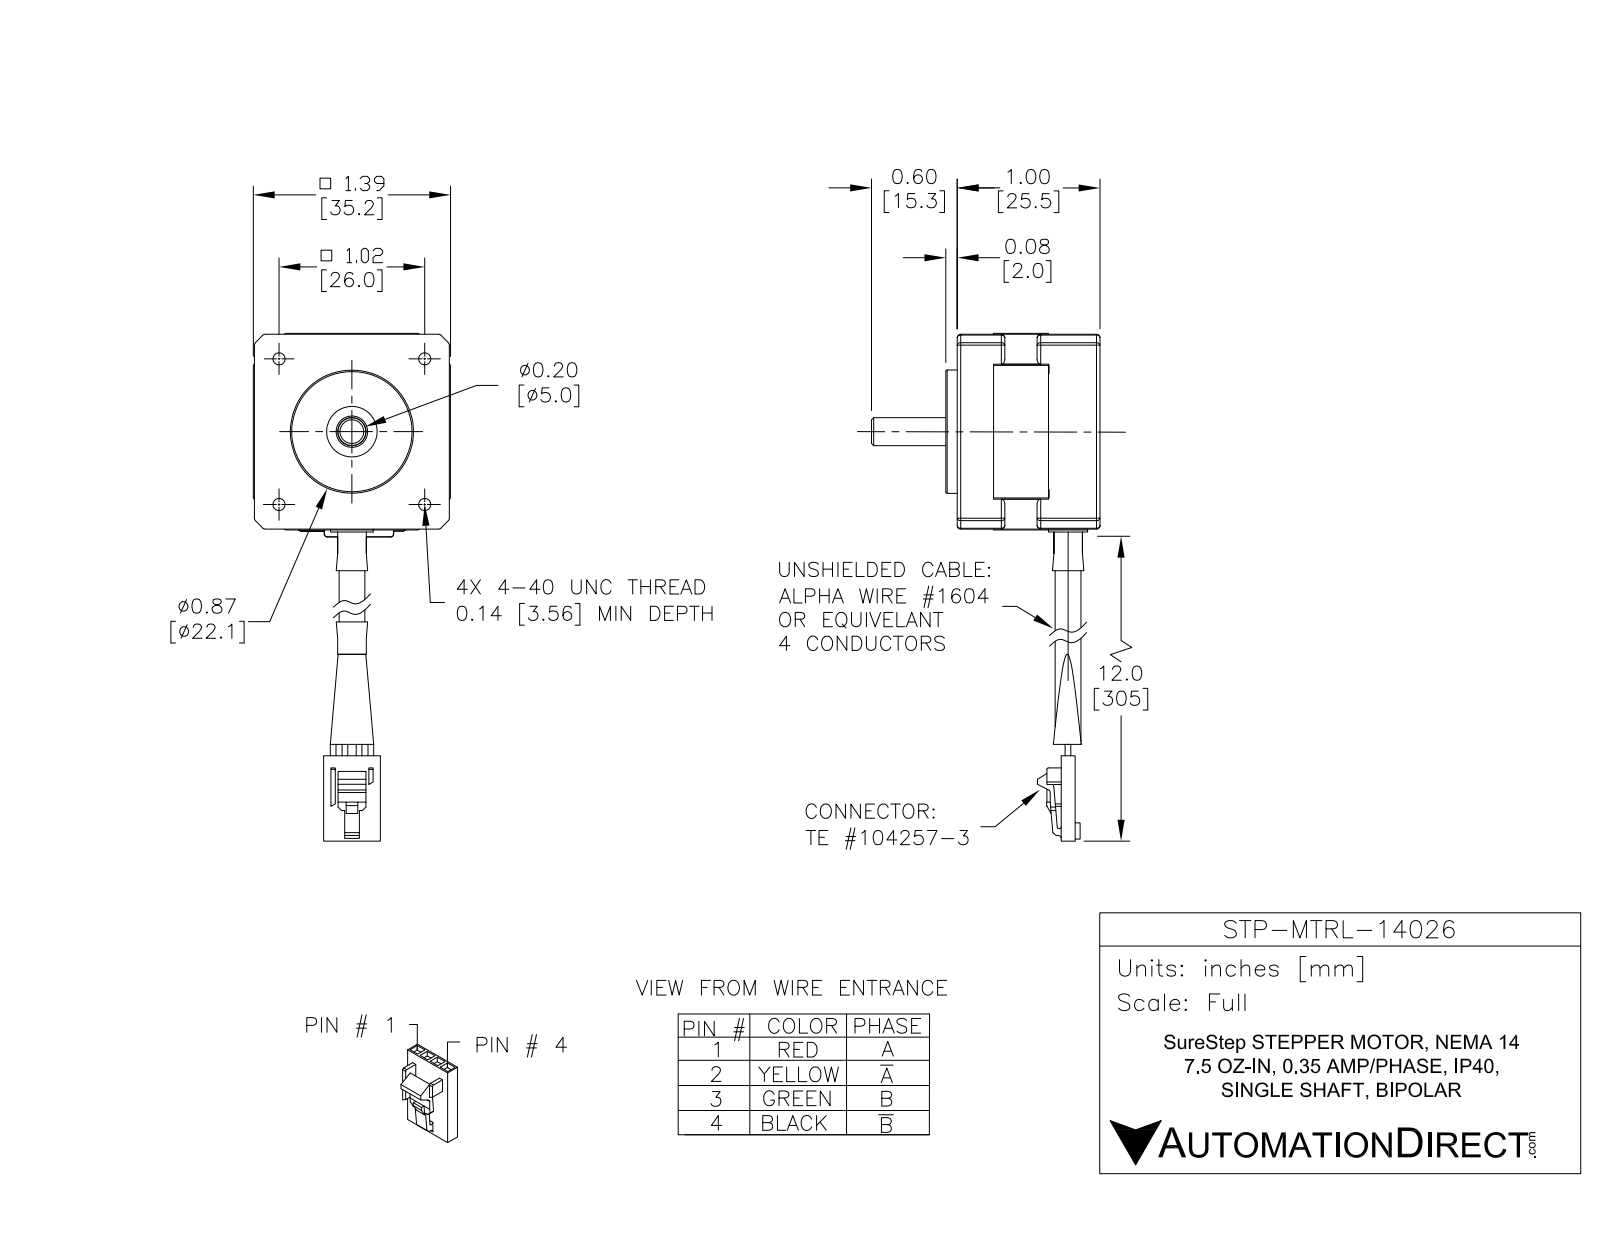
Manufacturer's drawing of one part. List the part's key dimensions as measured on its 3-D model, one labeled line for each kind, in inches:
Part name (STEP PRODUCT): STP-MTRL-14026
STEP written by: SolidWorks 2017 (AUTOMOTIVE_DESIGN)
Units: inches
Bodies: 12 solids, 564 faces (292 planar, 182 cylindrical, 90 other)
Overall size (bounding box): 13.447 × 1.606 × 1.381
Volume: 1.27 in³ · Surface area: 32.48 in²
Round holes (diameter × count): ⌀0.226 ×4, ⌀0.085 ×2, ⌀0.085 ×2, ⌀0.197 ×1, ⌀0.197 ×1, ⌀0.276 ×1, ⌀0.28 ×1, ⌀0.285 ×1, ⌀0.32 ×1, ⌀0.422 ×1, ⌀0.52 ×1, ⌀0.63 ×1
Round bosses / shafts (diameter × count): ⌀0.04 ×4, ⌀0.205 ×3, ⌀0.05 ×2, ⌀0.866 ×1, ⌀0.72 ×1, ⌀0.477 ×1, ⌀0.308 ×1, ⌀0.307 ×1
Partial cylindrical surfaces — rounded edges, fillets, slot ends (radius × count): R0.025 ×24, R0.02 ×10, R0.01 ×3, R0.014 ×1, R0.797 ×1, R0.798 ×1, R0.829 ×1, R0.833 ×1
Main face-to-face distances: 1.37, 1.376, 1.24, 0.065, 1.305, 1.004, 1.311, 0.07, 0.104, 0.041
Hole centre spacings: 0.724, 1.024, 1.448
